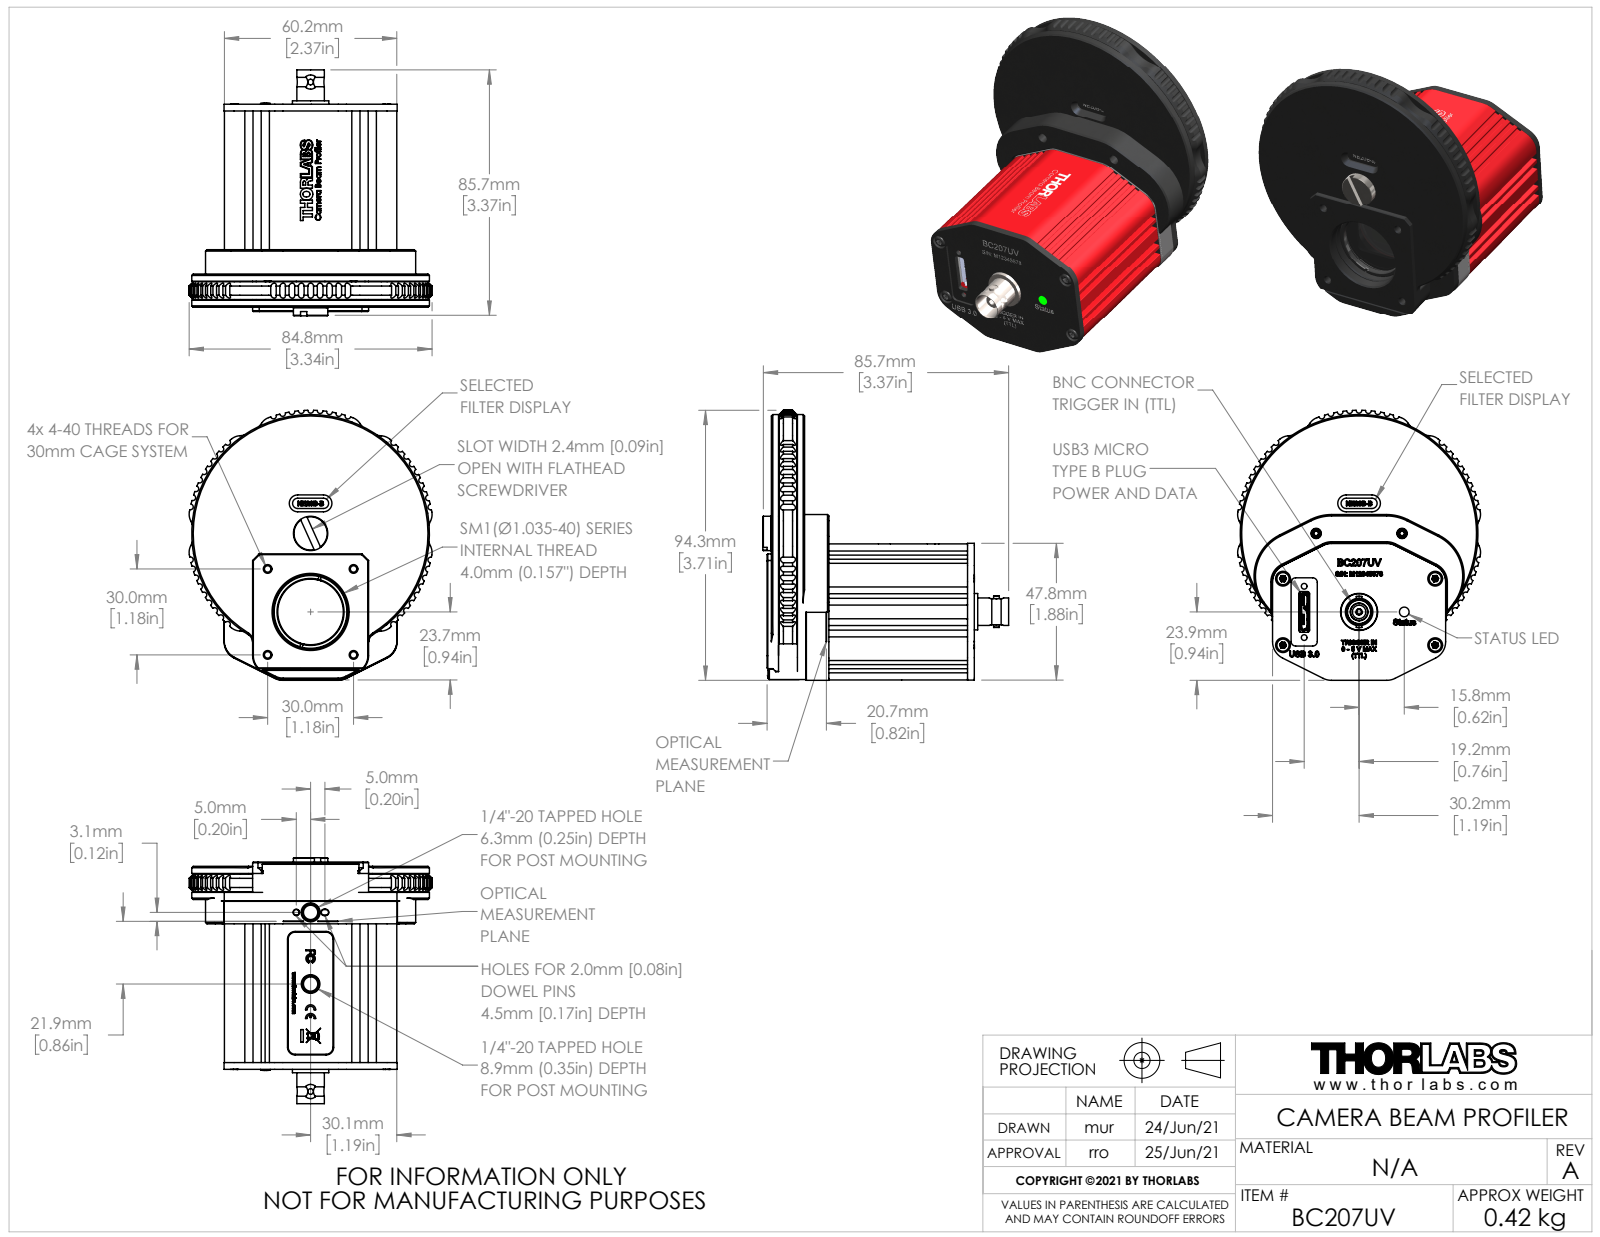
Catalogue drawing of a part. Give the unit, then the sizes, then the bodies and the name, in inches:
Units: inches
Overall size (bounding box): 3.711 × 3.38 × 3.341
Round holes (diameter × count): ⌀0.089 ×8, ⌀1.022 ×7, ⌀0.031 ×6, ⌀0.902 ×6, ⌀0.906 ×6, ⌀1.004 ×6, ⌀1.043 ×6, ⌀0.063 ×5, ⌀0.07 ×5, ⌀0.079 ×5, ⌀0.086 ×5, ⌀0.112 ×4
Round bosses / shafts (diameter × count): ⌀0.027 ×226, ⌀0.984 ×7, ⌀1.035 ×4, ⌀0.232 ×4, ⌀0.167 ×4, ⌀0.04 ×4, ⌀1.035 ×3, ⌀0.2 ×2
Partial cylindrical surfaces — rounded edges, fillets, slot ends (radius × count): R0.008 ×79, R0.039 ×58, R0.004 ×56, R0.006 ×48, R0.032 ×48, R0.02 ×28, R0.25 ×28, R0.032 ×24
Main face-to-face distances: 0.098, 0.358, 0.26, 0.335, 0.252, 0.35, 0.106, 0.378, 0.118, 0.476
Hole centre spacings: 0.591, 1.079, 1.181, 2.093, 0.475, 0.581, 0.598, 0.687
Volume: 8.759 in³ · Surface area: 165.6 in²
Bodies: 58 solids, 6105 faces (3321 planar, 1208 cylindrical, 1576 other)
Part name (STEP PRODUCT): 21.08.18_BC207UV_WEB
STEP written by: SolidWorks 2019 (AUTOMOTIVE_DESIGN)
